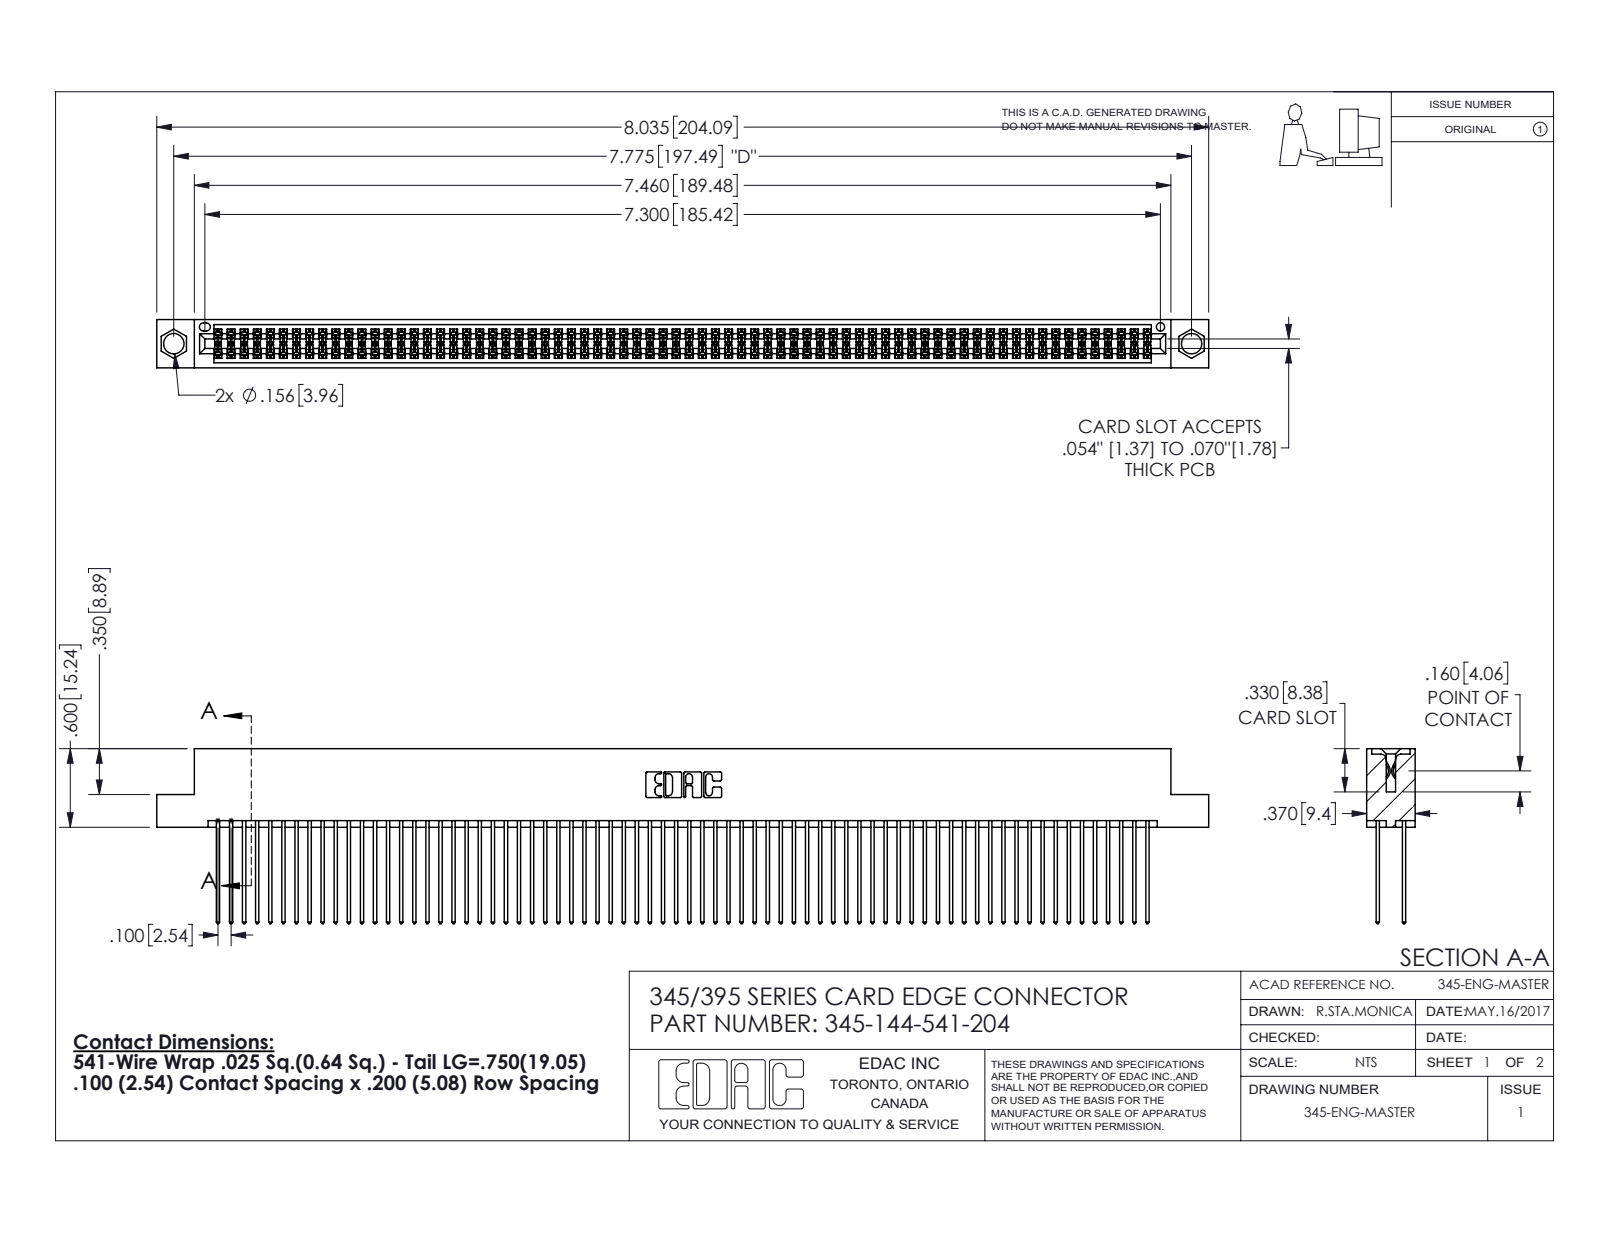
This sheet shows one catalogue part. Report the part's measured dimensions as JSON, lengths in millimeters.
{"part_name": "345-292-001_345-293-141; 345 Part_Flush Mounting Lugs - 0.156 Dia-TI; 345-144-541-204", "step_written_by": "SolidWorks 2020 (CONFIG_CONTROL_DESIGN)", "units": "millimeters", "bodies": {"solids": 145, "faces": 7340, "planar": 4846, "cylindrical": 2494, "other": 0}, "overall_size": [204.1, 34, 9.4], "volume_mm3": 20830, "surface_area_mm2": 35100, "round_holes": [[4, 2], [1.6, 1]], "partial_cylinders_radius": [[0.2, 288], [0.3, 144], [0.3, 22], [0.2, 6], [0.8, 6], [0.7, 3], [0.4, 2], [0.5, 2]], "face_to_face_distances": [1.8, 7.6, 5.1, 2.5, 6.9, 0.6, 5.7, 9.4, 4.4, 3.8], "hole_center_spacings": [6.9, 191.5, 197.5]}
